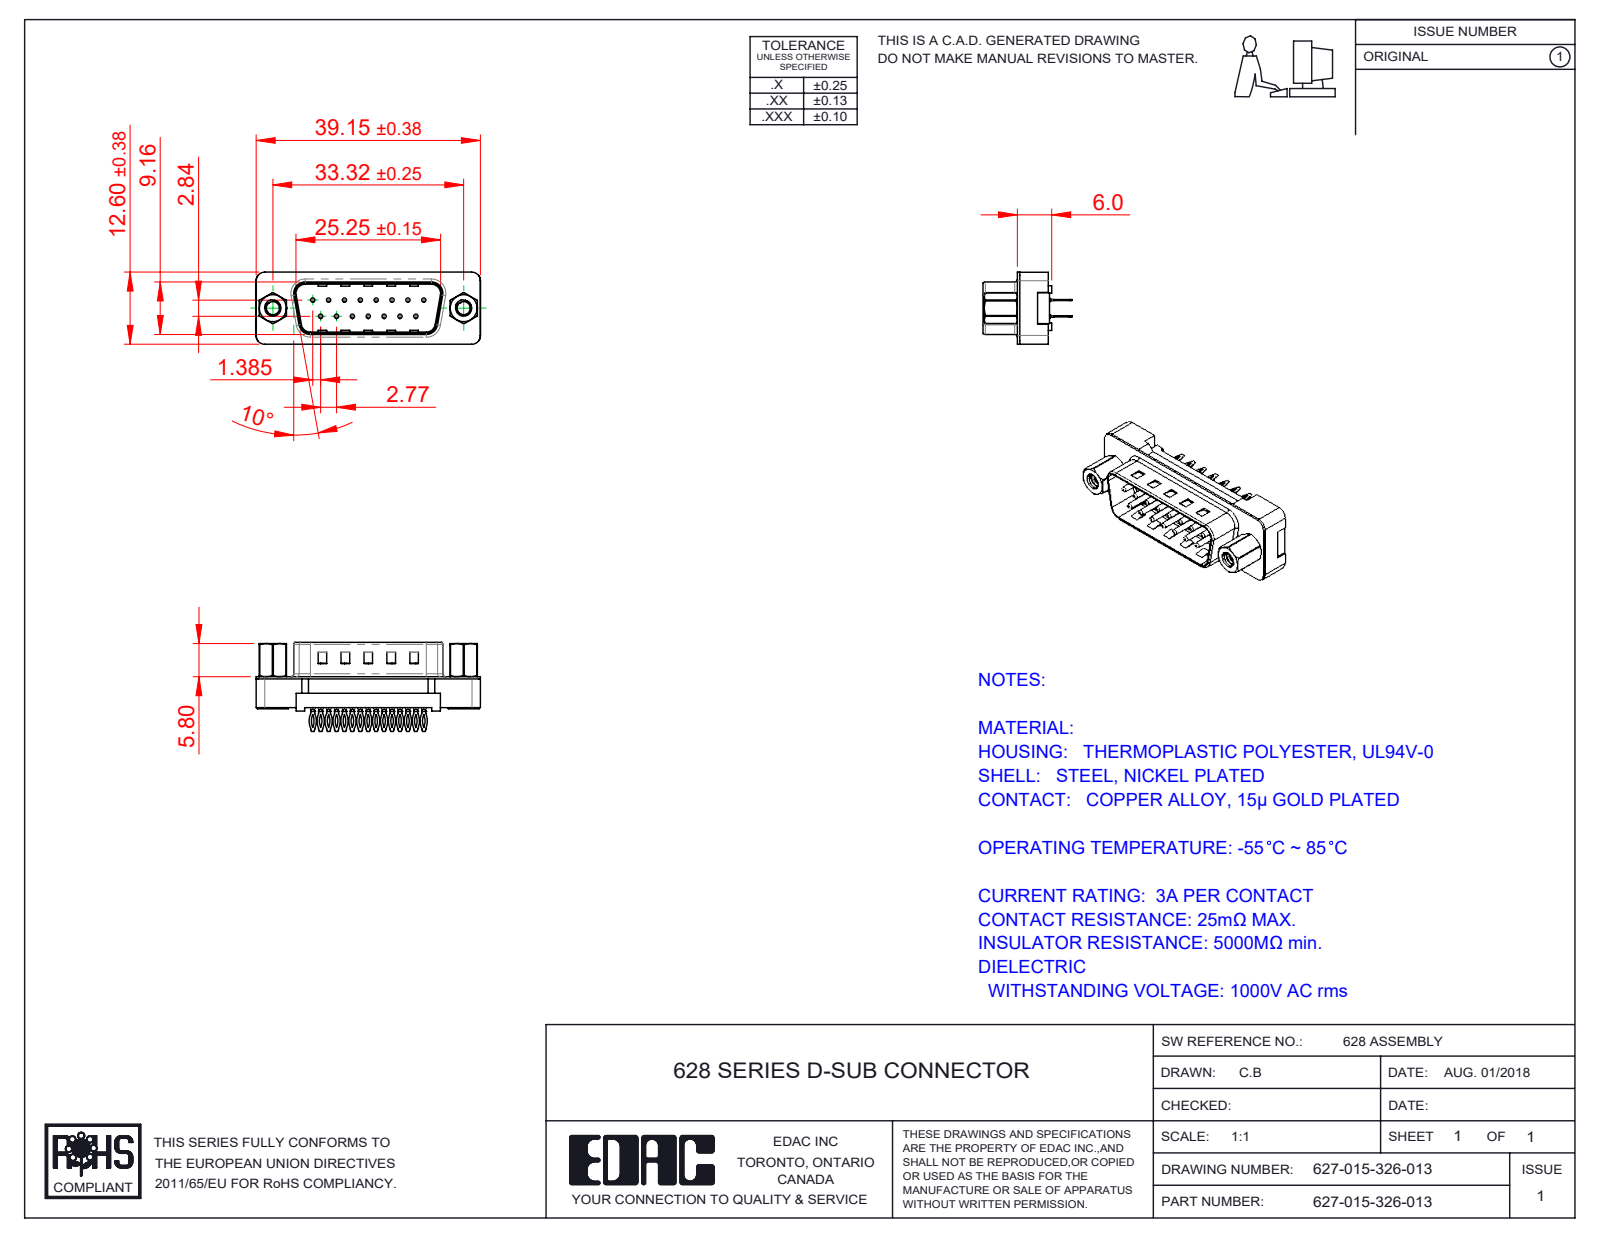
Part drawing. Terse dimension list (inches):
name: 627 PB Contact Row 2_26; 627 PB Shell_15 Contacts; 627 4-40 Hex Standoff; 627-015-326-013 (+3 more)
written by: SolidWorks 2020 (CONFIG_CONTROL_DESIGN)
unit: in
bodies: 21 solids, 1482 faces (838 planar, 472 cylindrical, 172 other)
size: 1.543 × 0.612 × 0.496
volume: 0.134 in³; area: 7.369 in²
holes: 15× ⌀0.014, 15× ⌀0.033, 2× ⌀0.089, 2× ⌀0.09, 2× ⌀0.157, 2× ⌀0.189, 2× ⌀0.197
bosses: 15× ⌀0.03, 2× ⌀0.193, 2× ⌀0.11
rounds: 30× R0.01, 30× R0.115, 30× R0.131, 15× R0.005, 8× R0.02, 8× R0.059, 4× R0.035, 4× R0.063
face distances: 0.016, 0.098, 0.213, 0.345, 0.197, 0.114, 0.187, 0.256, 0.334, 0.027
hole spacings: 0.124, 0.109, 0.218, 0.327, 0.198, 0.294, 0.436, 0.198
